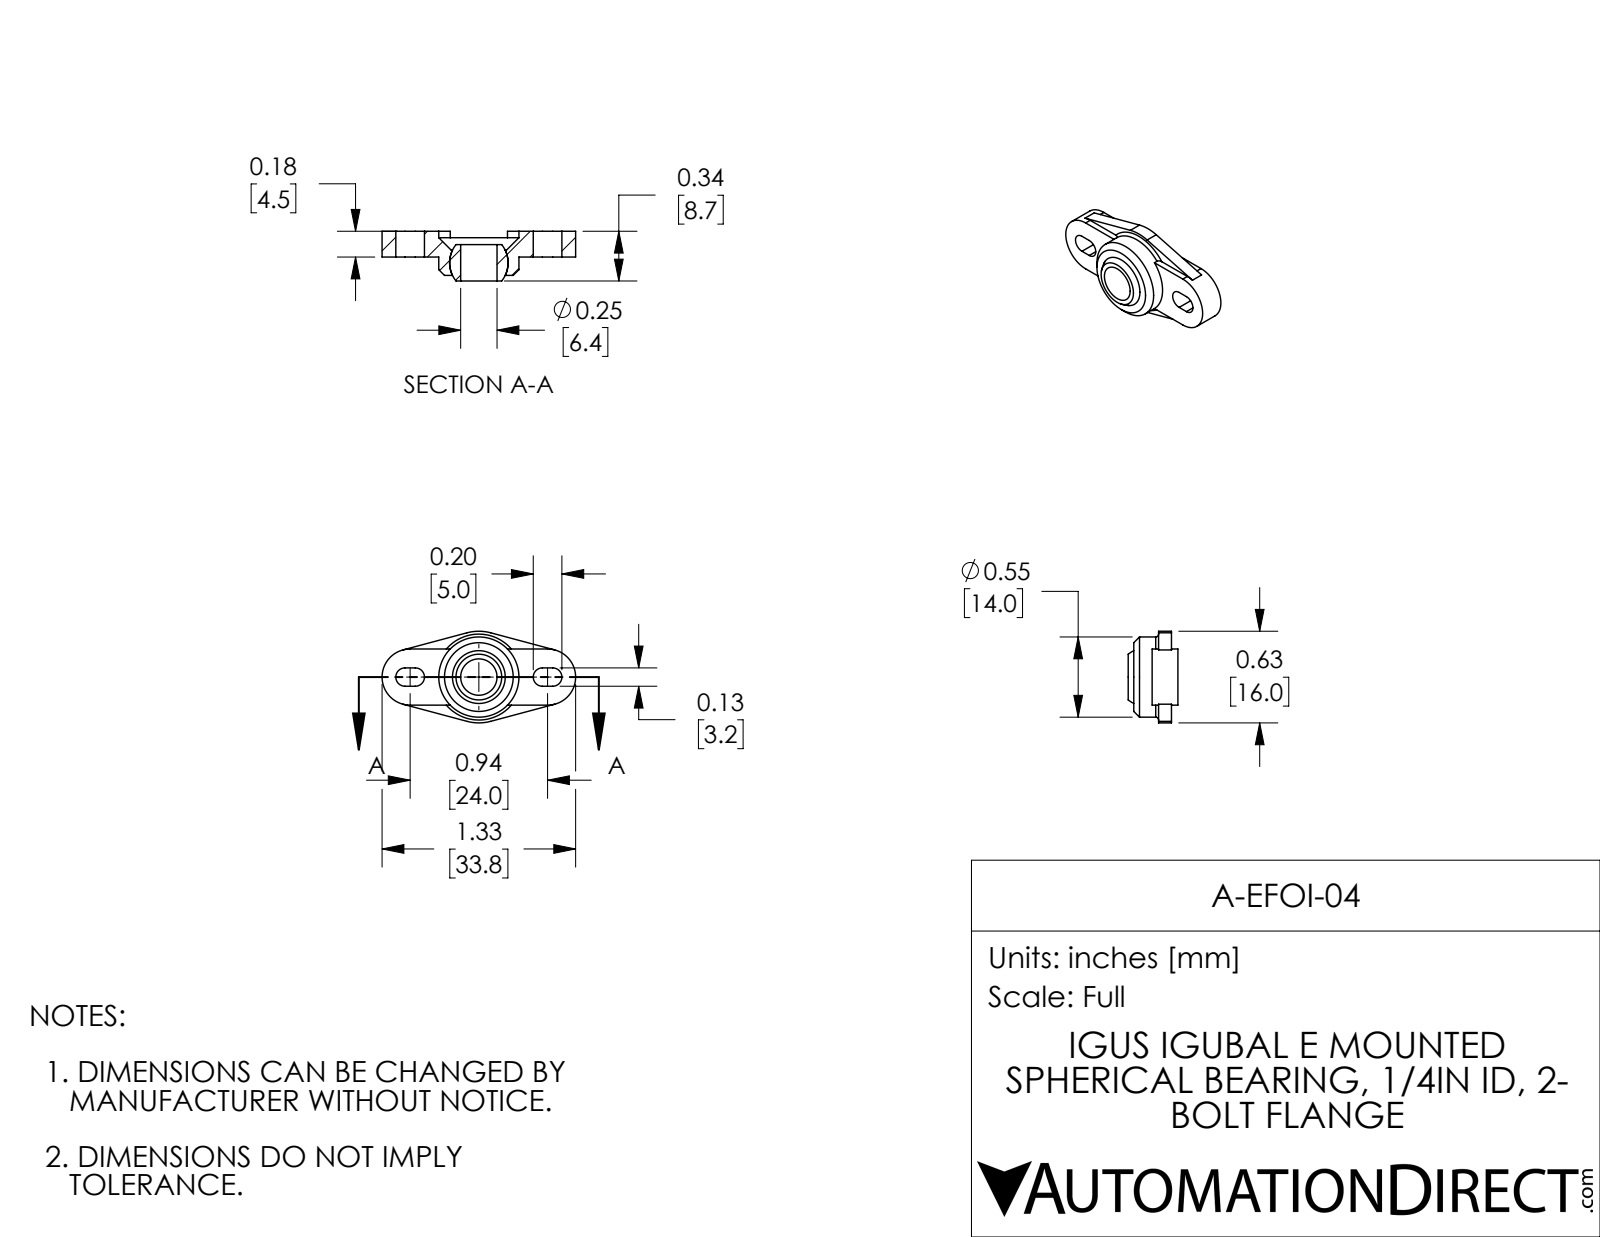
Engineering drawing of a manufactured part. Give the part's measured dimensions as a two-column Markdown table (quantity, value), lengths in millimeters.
| quantity | value |
| --- | --- |
| part name | A-EFOI-04 |
| STEP written by | SolidWorks 2017 (AUTOMOTIVE_DESIGN) |
| units | millimeters |
| bodies | 2 solids, 56 faces (28 planar, 18 cylindrical, 10 other) |
| overall size | 33.8 × 16 × 10.4 |
| volume | 1 500 mm³ |
| surface area | 1 738 mm² |
| round holes (diameter × count) | 6.4 × 1, 14 × 1 |
| partial cylindrical surfaces (radius × count) | 1.6 × 4, 4.9 × 2, 8 × 1 |
| main face-to-face distances | 4.5, 1.1, 3.4, 3.2, 16, 7.7, 6.6, 2.3, 4.3, 3.3 |
